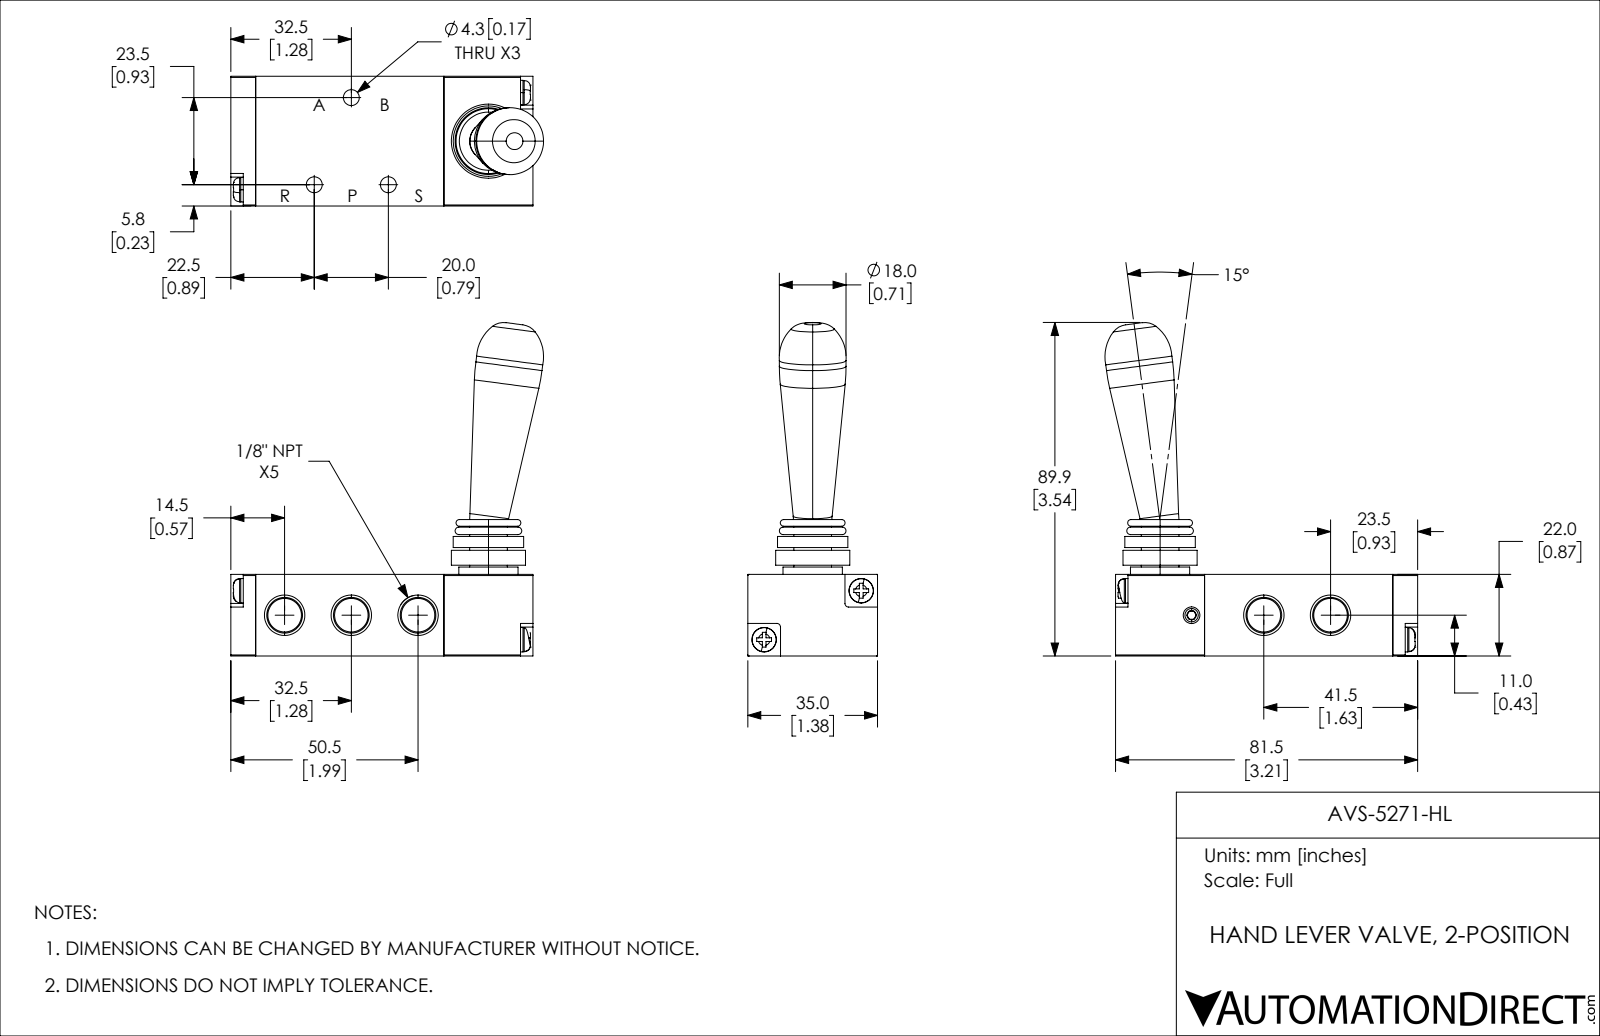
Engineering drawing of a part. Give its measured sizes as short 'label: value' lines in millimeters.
name: AVS-5271-HL
written by: SolidWorks 2018 (AUTOMOTIVE_DESIGN)
unit: mm
bodies: 4 solids, 228 faces (128 planar, 56 cylindrical, 44 other)
size: 89.95 × 84.39 × 35
volume: 69 999 mm³; area: 21 794 mm²
holes: 3× ⌀4.3, 1× ⌀4.5, 1× ⌀16
bosses: 4× ⌀6.6, 4× ⌀6.5, 1× ⌀20, 1× ⌀19, 1× ⌀18, 1× ⌀10.16, 1× ⌀3.6
rounds: 4× R0.3, 4× R1
face distances: 22, 35, 50.8, 24, 74.8, 2, 6.7, 81.5, 57.5, 4
hole spacings: 25.54, 20, 29.45, 38.82, 48.45
